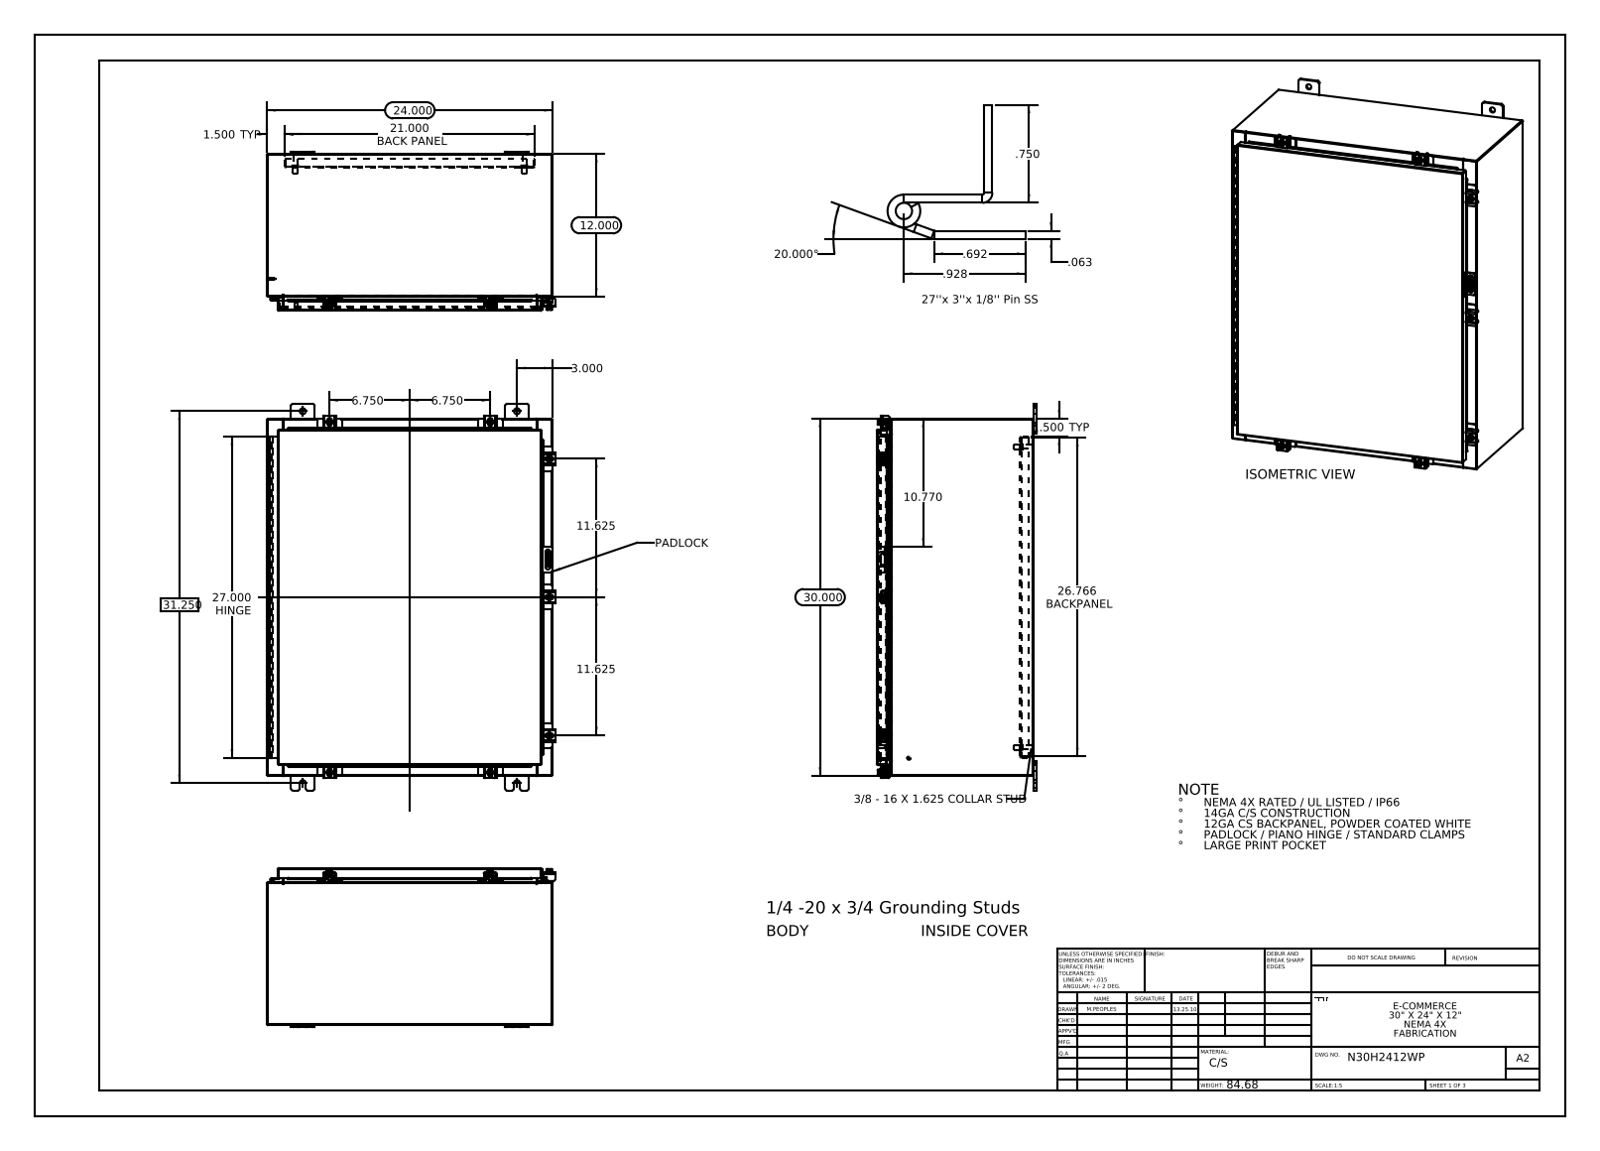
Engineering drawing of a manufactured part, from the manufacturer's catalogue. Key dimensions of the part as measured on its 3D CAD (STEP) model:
Part name (STEP PRODUCT): N30H2412SSWP Clamp Bracket; N30H2412SSWP 22101002; N30H2412SSWP Top; N30H2412SSWP Cover (+8 more)
STEP written by: SolidWorks 2013 (CONFIG_CONTROL_DESIGN)
Units: inches
Bodies: 54 solids, 2016 faces (1062 planar, 838 cylindrical, 116 other)
Overall size (bounding box): 32.5 × 24.211 × 13.389
Volume: 297 in³ · Surface area: 7 481 in²
Round holes (diameter × count): ⌀0.5 ×8, ⌀0.213 ×7, ⌀0.26 ×7, ⌀0.125 ×2
Round bosses / shafts (diameter × count): ⌀0.25 ×8, ⌀0.5 ×7, ⌀0.399 ×7, ⌀0.625 ×4, ⌀0.375 ×4, ⌀0.33 ×4, ⌀0.315 ×2, ⌀0.236 ×2
Partial cylindrical surfaces — rounded edges, fillets, slot ends (radius × count): R0.06 ×34, R0.013 ×27, R0.19 ×24, R0.088 ×21, R0.12 ×14, R0.141 ×14, R0.05 ×11, R0.08 ×10
Main face-to-face distances: 0.075, 13.126, 23.925, 13.051, 13.201, 0.104, 1, 29.925, 1.075, 12.051
Hole centre spacings: 27.501, 31.878, 1.858, 2.277, 2.326, 2.423, 3.561, 3.561
